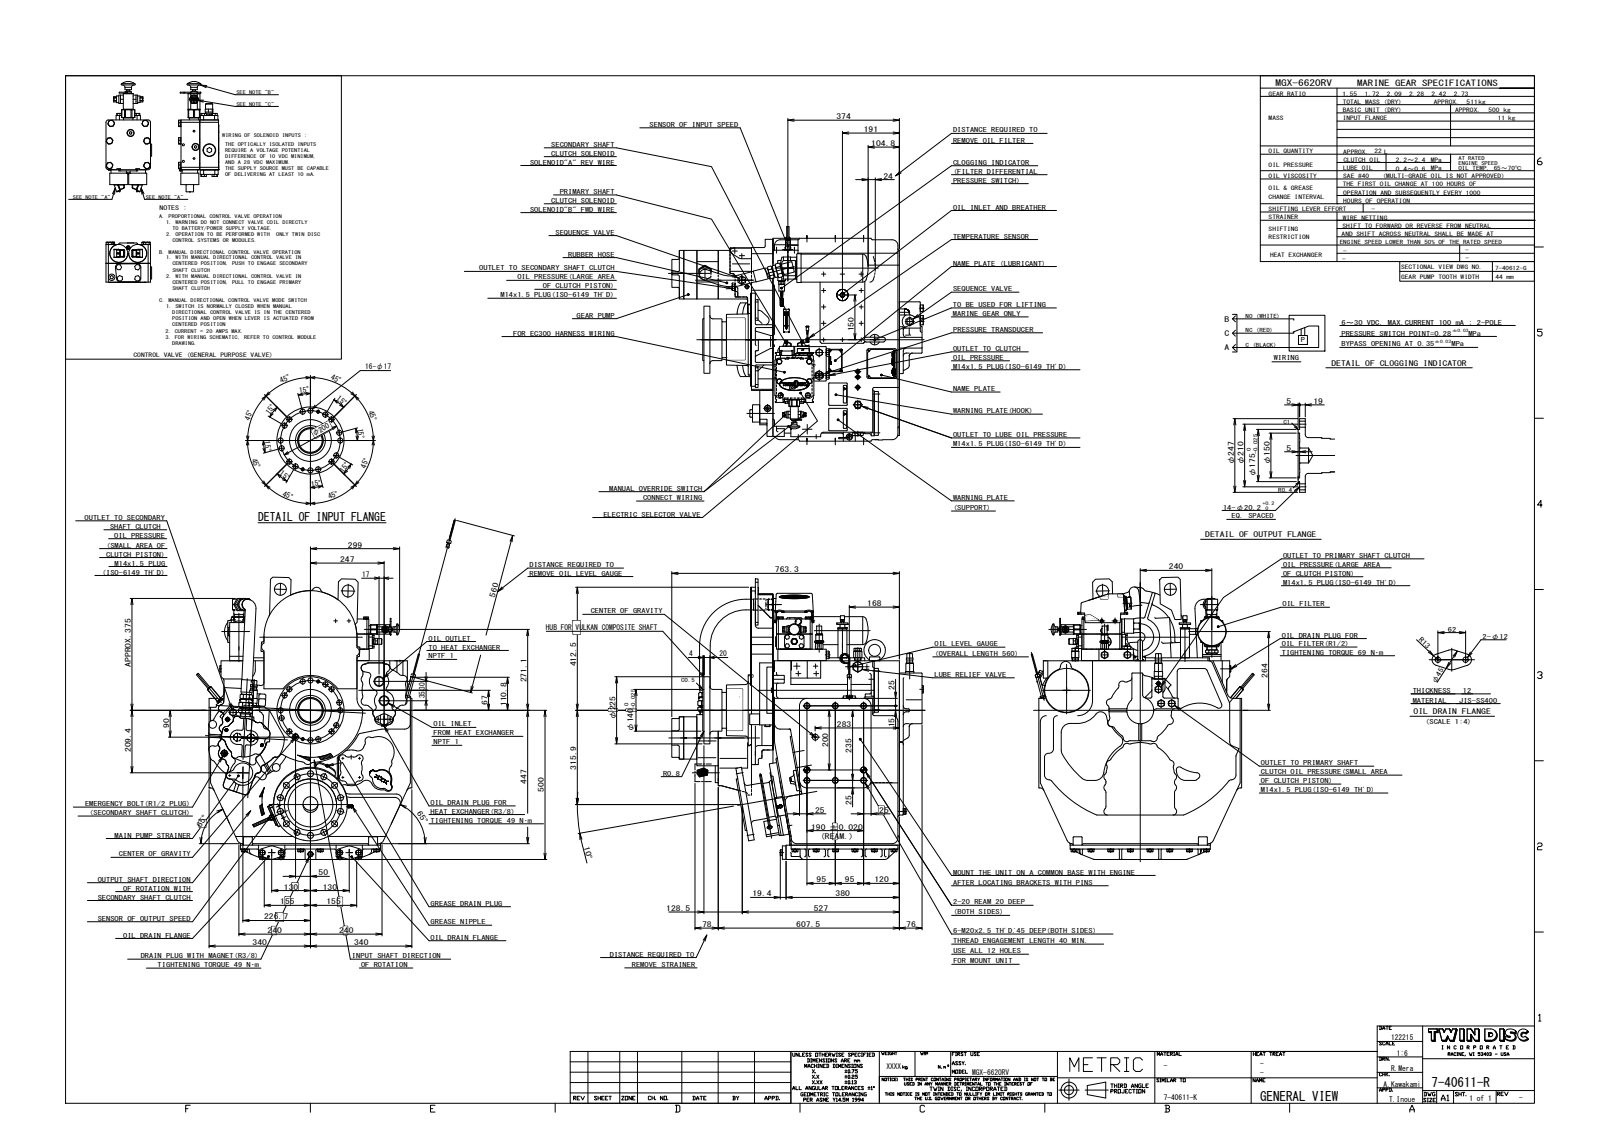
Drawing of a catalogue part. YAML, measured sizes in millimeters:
part_name: "740611R"
step_written_by: "SolidWorks 2015 (AUTOMOTIVE_DESIGN)"
units: millimeters
bodies: {solids: 0, faces: 3883, planar: 1489, cylindrical: 1649, other: 745}
overall_size: [947.44, 841.5, 742.49]
round_holes:
  - {diameter: 11, count: 34}
  - {diameter: 17, count: 16}
  - {diameter: 20.3, count: 14}
  - {diameter: 12, count: 11}
  - {diameter: 20, count: 10}
  - {diameter: 9, count: 8}
  - {diameter: 3, count: 5}
  - {diameter: 8, count: 4}
  - {diameter: 10, count: 4}
  - {diameter: 13, count: 4}
  - {diameter: 19, count: 4}
  - {diameter: 28, count: 4}
round_bosses_or_shafts:
  - {diameter: 21, count: 25}
  - {diameter: 2.54, count: 5}
  - {diameter: 15.7, count: 4}
  - {diameter: 38, count: 3}
  - {diameter: 35, count: 3}
  - {diameter: 120, count: 2}
  - {diameter: 48.26, count: 2}
  - {diameter: 47.45, count: 2}
partial_cylinders:
  - {radius: 10, count: 179}
  - {radius: 2, count: 80}
  - {radius: 5, count: 64}
  - {radius: 12, count: 60}
  - {radius: 13, count: 58}
  - {radius: 0.5, count: 18}
  - {radius: 14, count: 18}
  - {radius: 20, count: 18}
face_to_face_distances: [5, 72, 424, 496, 419, 491, 618, 48, 13, 3.2]
hole_center_spacings: [46.73, 130.93, 141.42, 100, 121.75, 158.67, 173.2, 51.76]
